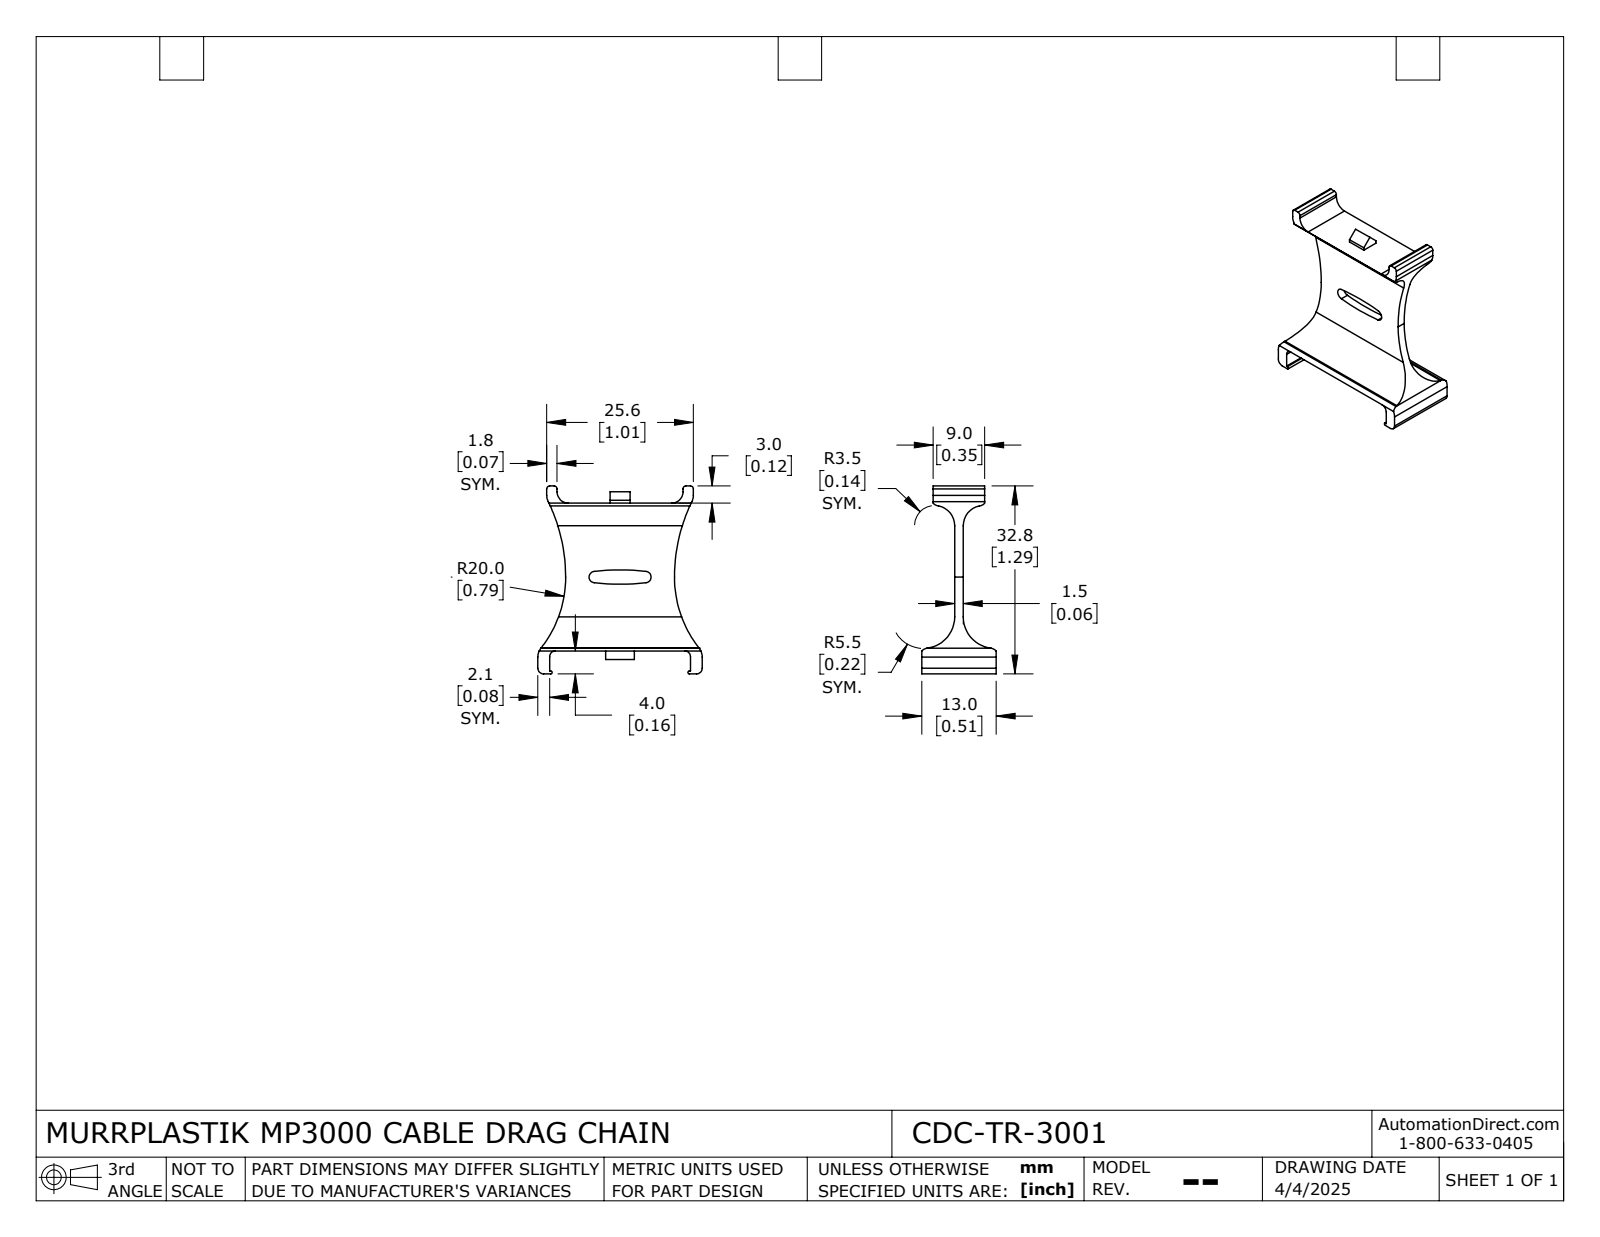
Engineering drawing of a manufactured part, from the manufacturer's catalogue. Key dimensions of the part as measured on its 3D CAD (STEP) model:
Part name (STEP PRODUCT): CDC-TR-3001
STEP written by: SolidWorks 2024 (AUTOMOTIVE_DESIGN)
Units: millimetres
Bodies: 1 solid, 70 faces (38 planar, 32 cylindrical, 0 other)
Overall size (bounding box): 32.8 × 28.7 × 13
Volume: 1 814 mm³ · Surface area: 2 474 mm²
Partial cylindrical surfaces — rounded edges, fillets, slot ends (radius × count): R1 ×6, R0.5 ×4, R1.5 ×4, R2.5 ×4, R0.25 ×2, R2 ×2, R3.5 ×2, R5.5 ×2
Main face-to-face distances: 1.5, 25.8, 2.05, 26.65, 5.75, 7.25, 24.6, 4, 29.8, 0.5
